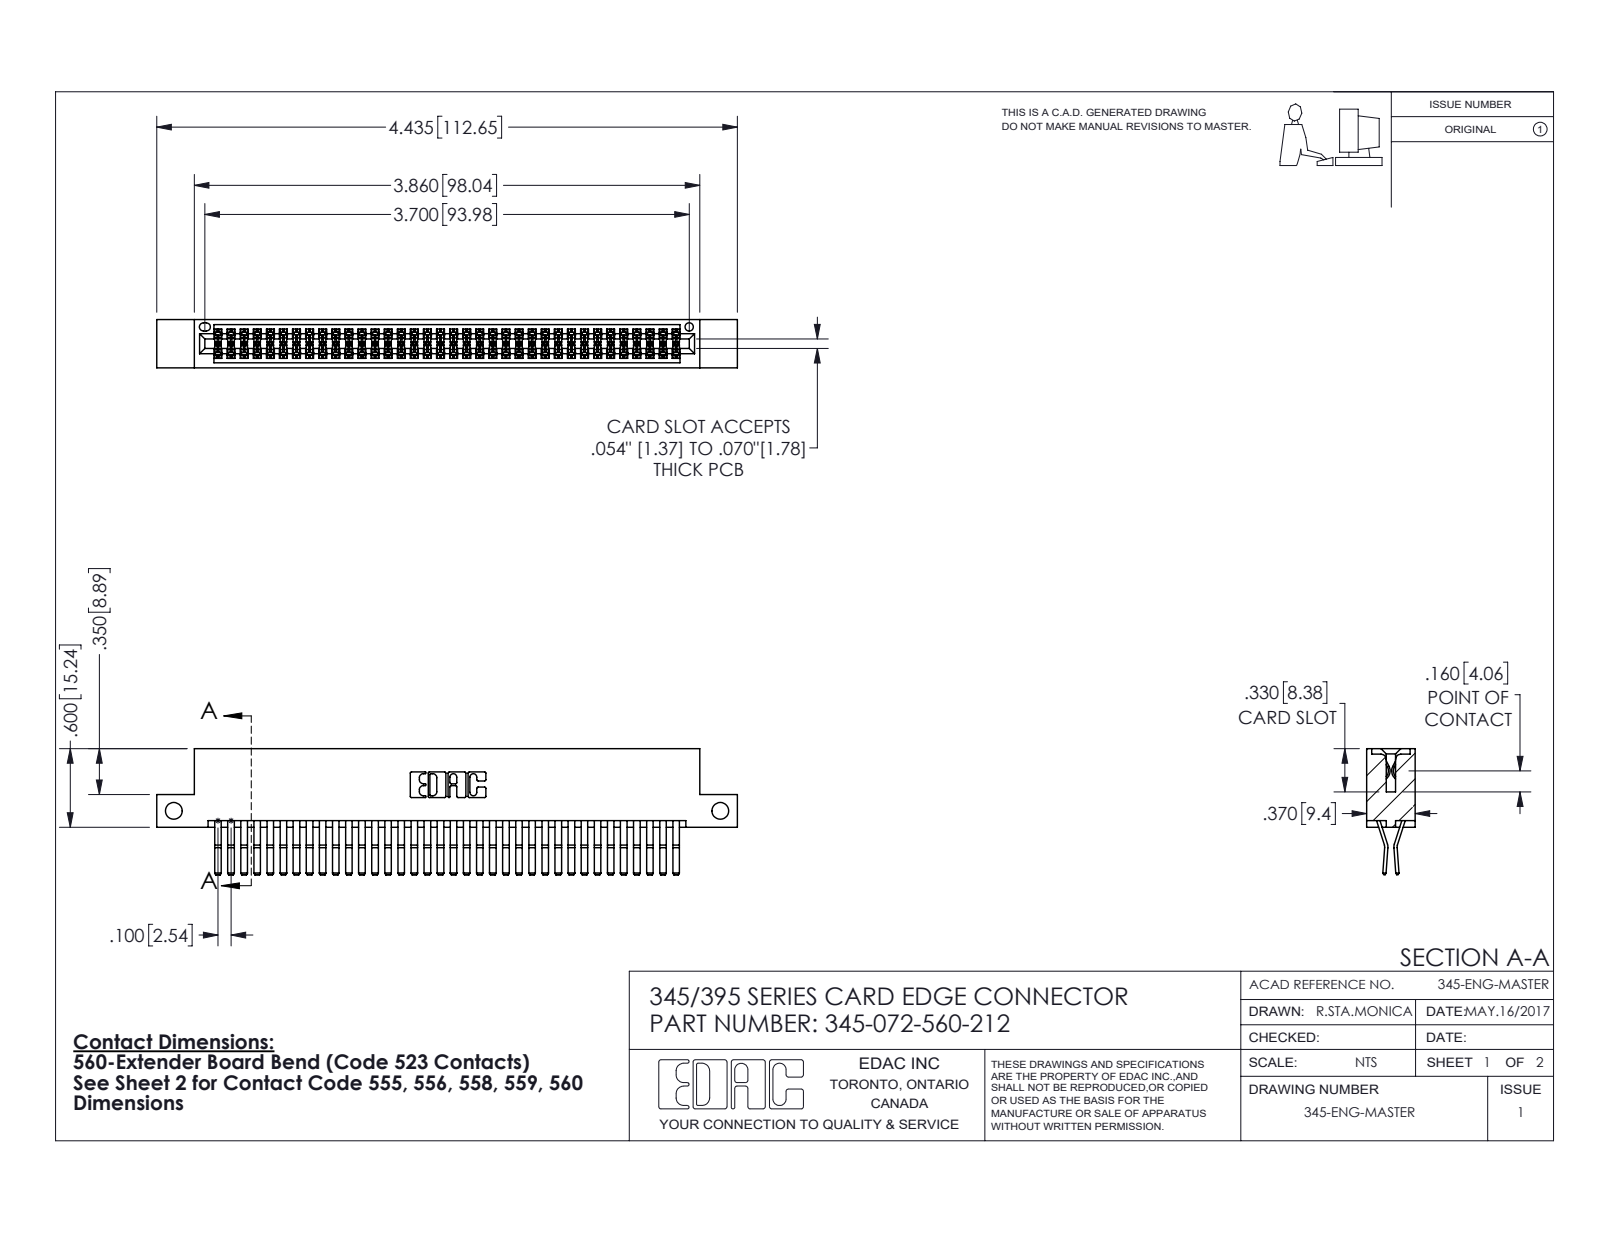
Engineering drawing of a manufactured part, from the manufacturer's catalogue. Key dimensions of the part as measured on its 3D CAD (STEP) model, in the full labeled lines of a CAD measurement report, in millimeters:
Part name (STEP PRODUCT): 345-072-560-212; 345-292-001_560 Tail; 345 Part_Flush Mounting Lugs - Side Mount
STEP written by: SolidWorks 2016 (CONFIG_CONTROL_DESIGN)
Units: millimetres
Bodies: 73 solids, 3870 faces (2456 planar, 1414 cylindrical, 0 other)
Overall size (bounding box): 112.6 × 24.4 × 9.4
Volume: 11 300 mm³ · Surface area: 17 630 mm²
Round holes (diameter × count): ⌀3.3 ×2, ⌀1.6 ×1
Partial cylindrical surfaces — rounded edges, fillets, slot ends (radius × count): R0.2 ×108, R0.3 ×22, R0.2 ×6, R0.8 ×6, R0.7 ×3, R0.3 ×2, R0.4 ×2, R0.5 ×2
Main face-to-face distances: 0.6, 7.6, 1.8, 5.1, 9.4, 2.5, 6.9, 5.7, 4.4, 3.8
Hole centre spacings: 106
